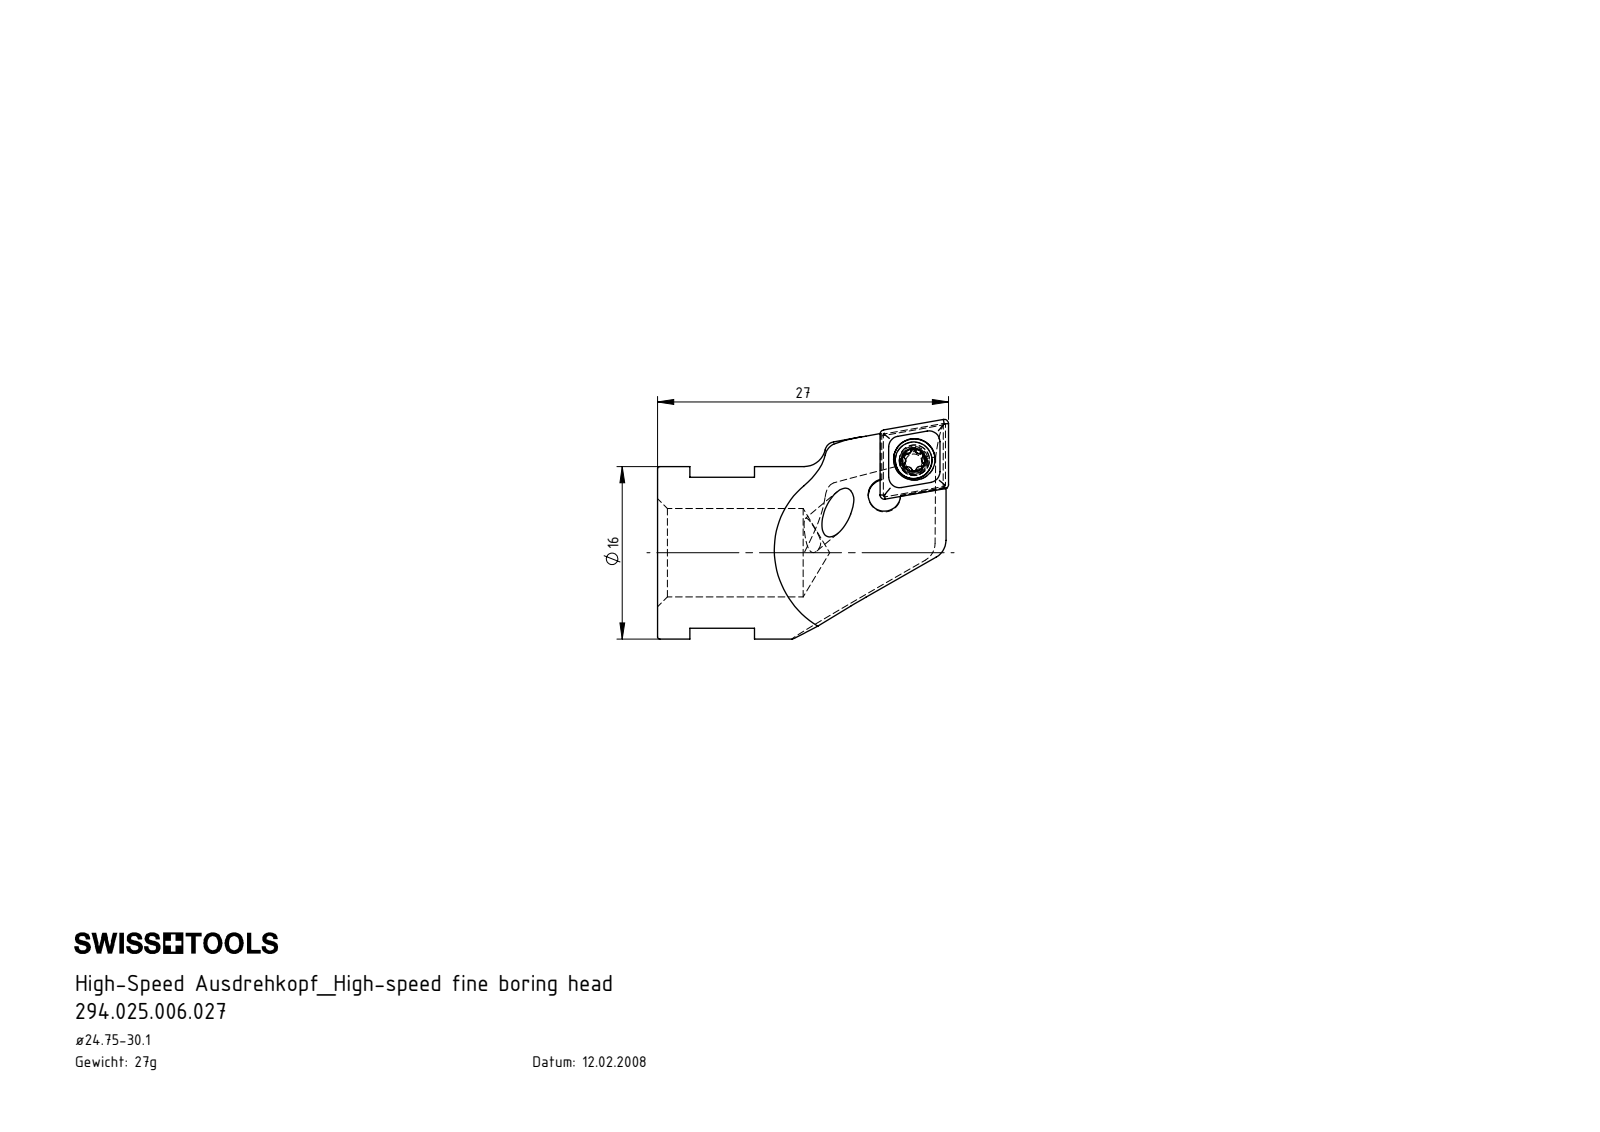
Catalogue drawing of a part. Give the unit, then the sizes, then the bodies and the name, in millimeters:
Units: millimetres
Overall size (bounding box): 27 × 20.38 × 16
Round holes (diameter × count): ⌀2.05 ×1, ⌀2.8 ×1, ⌀3 ×1, ⌀3.85 ×1, ⌀8.2 ×1
Round bosses / shafts (diameter × count): ⌀16 ×1, ⌀3.4 ×1, ⌀2.5 ×1
Partial cylindrical surfaces — rounded edges, fillets, slot ends (radius × count): R0.21 ×6, R0.36 ×5, R0.36 ×1, R1.5 ×1, R1.8 ×1, R2 ×1
Main face-to-face distances: 2.28, 14, 6, 2.38, 3, 9, 20.8, 17.8, 11.8, 1.48
Volume: 3 373 mm³ · Surface area: 2 198 mm²
Bodies: 3 solids, 121 faces (34 planar, 35 cylindrical, 52 other)
Part name (STEP PRODUCT): WCA-ER2.001.006_A; CCMT060204; HS0-A25.K11.027_B; HS0.A25.K11.027
STEP written by: SolidWorks 2017 (AUTOMOTIVE_DESIGN)
